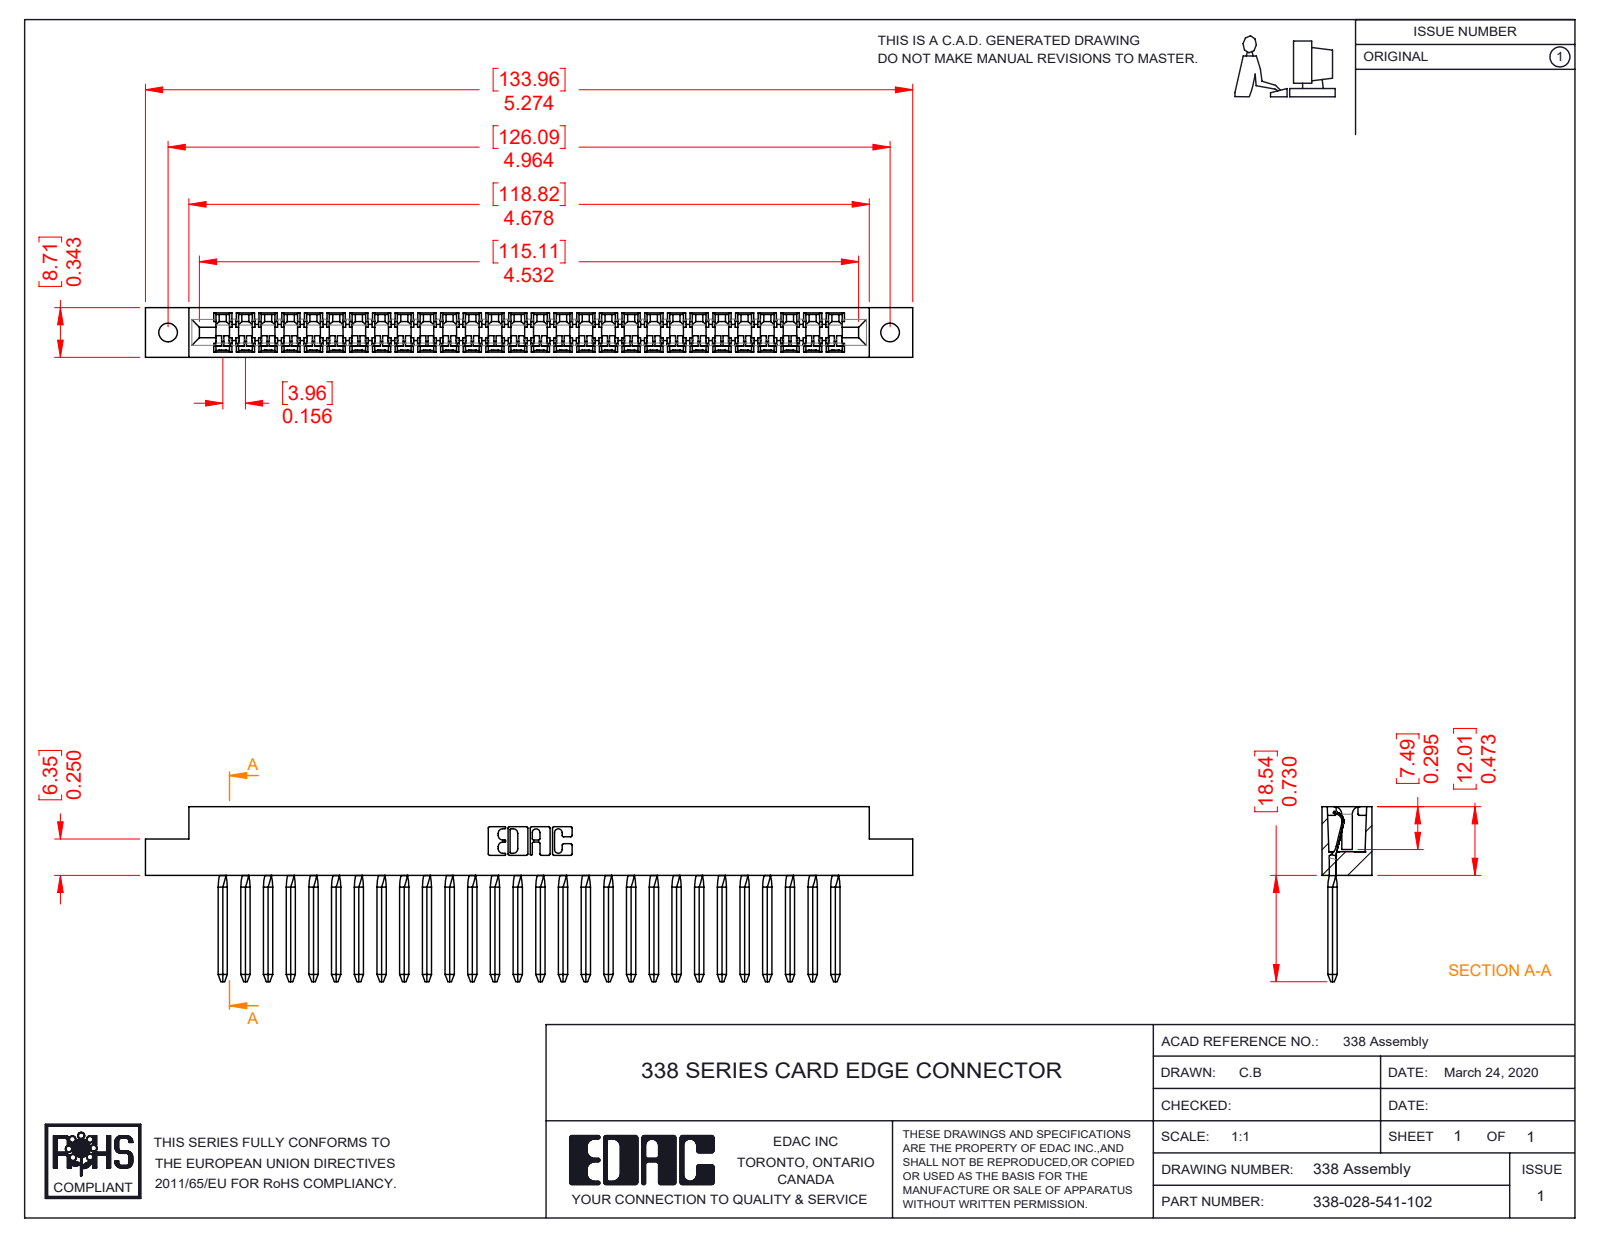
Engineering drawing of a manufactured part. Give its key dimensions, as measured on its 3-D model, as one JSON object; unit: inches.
{"part_name": "338-028-541-102; 338-210-001_338-210-028-002; 338-290-001_541", "step_written_by": "SolidWorks 2016 (CONFIG_CONTROL_DESIGN)", "units": "inches", "bodies": {"solids": 29, "faces": 2698, "planar": 1870, "cylindrical": 716, "other": 112}, "overall_size": [5.274, 1.203, 0.343], "volume_in3": 0.571, "surface_area_in2": 23.37, "round_holes": [[0.128, 2]], "partial_cylinders_radius": [[0.025, 114], [0.008, 28], [0.055, 23], [0.067, 23], [0.01, 22], [0.1, 22], [0.007, 6], [0.031, 6]], "face_to_face_distances": [0.343, 0.156, 0.11, 0.207, 0.135, 0.624, 0.78, 0.468, 0.048, 0.072], "hole_center_spacings": [4.964]}
